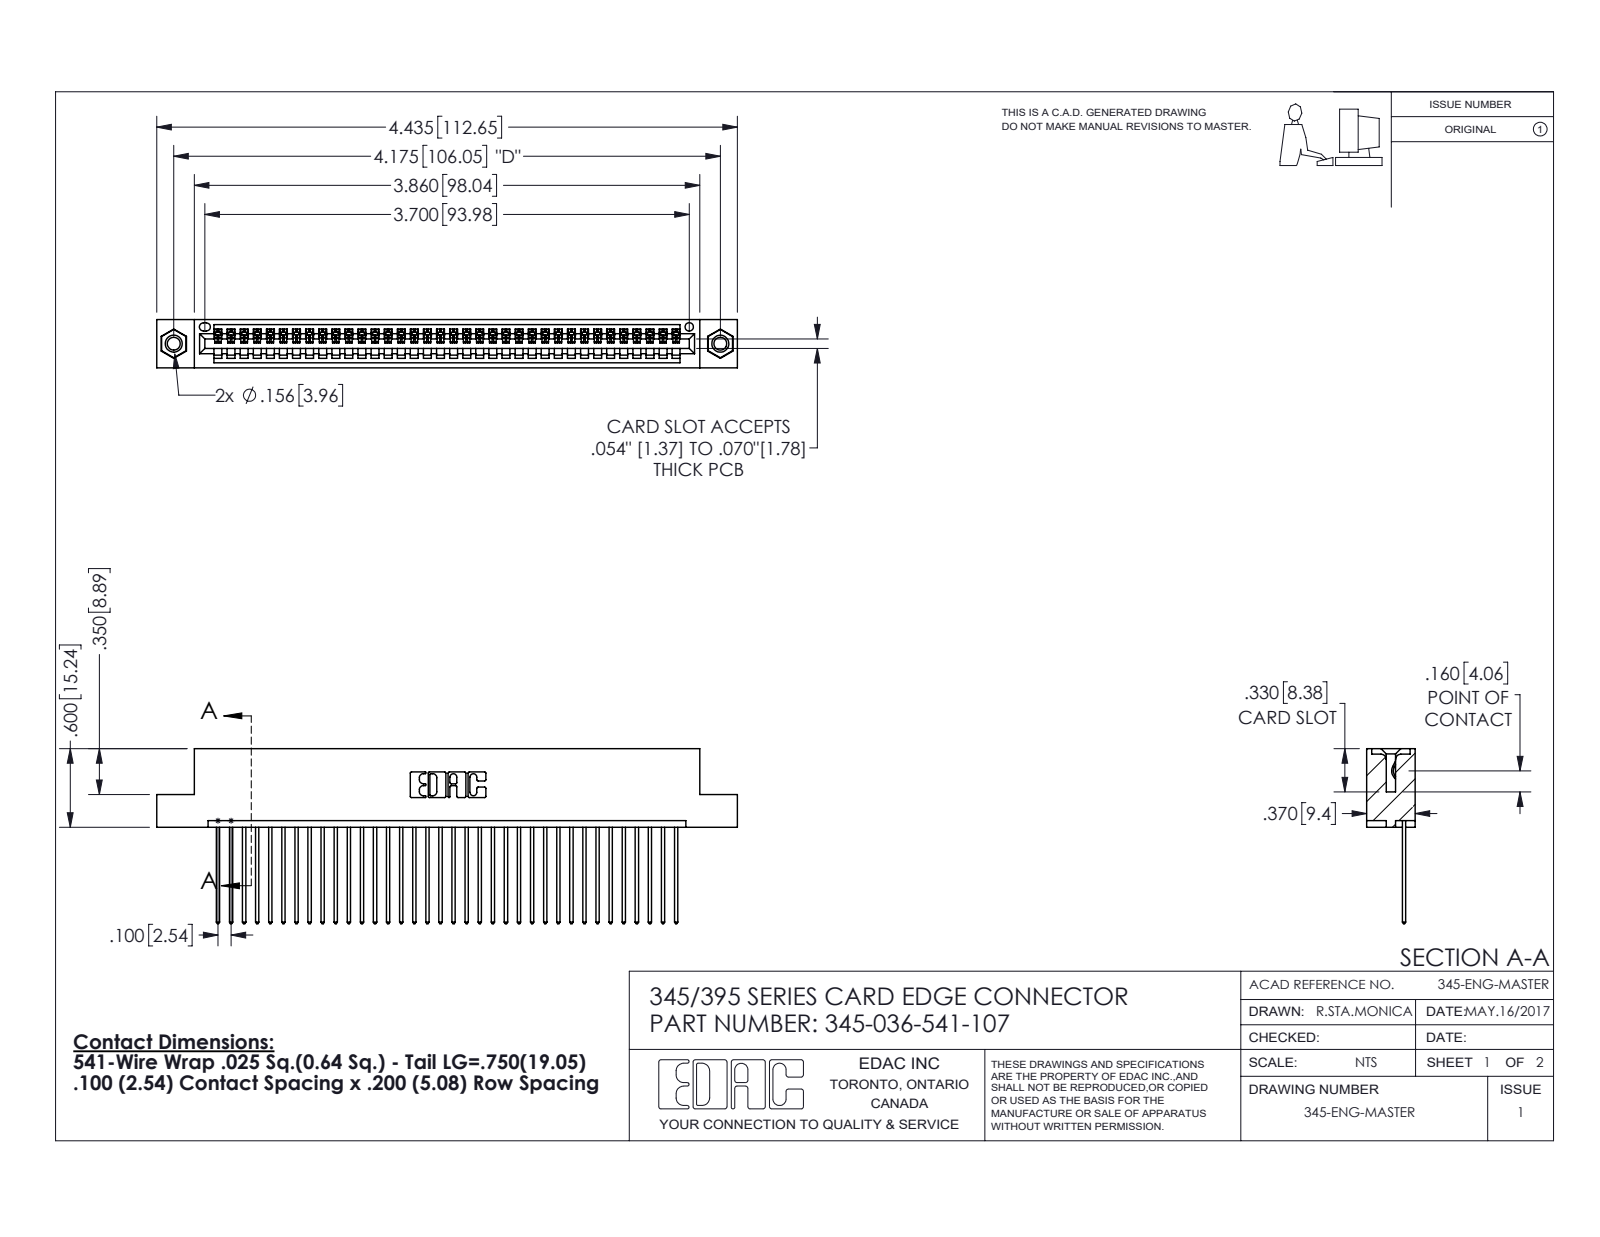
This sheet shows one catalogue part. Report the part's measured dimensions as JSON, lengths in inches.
{"part_name": "345-250-001_345-250-005-103; 345-036-541-107; 345-292-001_345-293-141; 345 Part_Flush Mounting Lugs - 0.156 Dia-TI", "step_written_by": "SolidWorks 2016 (CONFIG_CONTROL_DESIGN)", "units": "inches", "bodies": {"solids": 39, "faces": 2274, "planar": 1552, "cylindrical": 706, "other": 16}, "overall_size": [4.435, 1.337, 0.37], "volume_in3": 0.656, "surface_area_in2": 23.16, "round_holes": [[0.098, 2], [0.125, 2], [0.156, 2], [0.064, 1]], "round_bosses_or_shafts": [[0.155, 2]], "partial_cylinders_radius": [[0.006, 72], [0.01, 72], [0.01, 22], [0.007, 6], [0.031, 6], [0.026, 3], [0.031, 2], [0.04, 2]], "face_to_face_distances": [0.072, 0.298, 0.098, 0.272, 0.025, 0.37, 0.2, 0.225, 0.149, 0.072], "hole_center_spacings": [0.27, 3.939, 4.175]}
